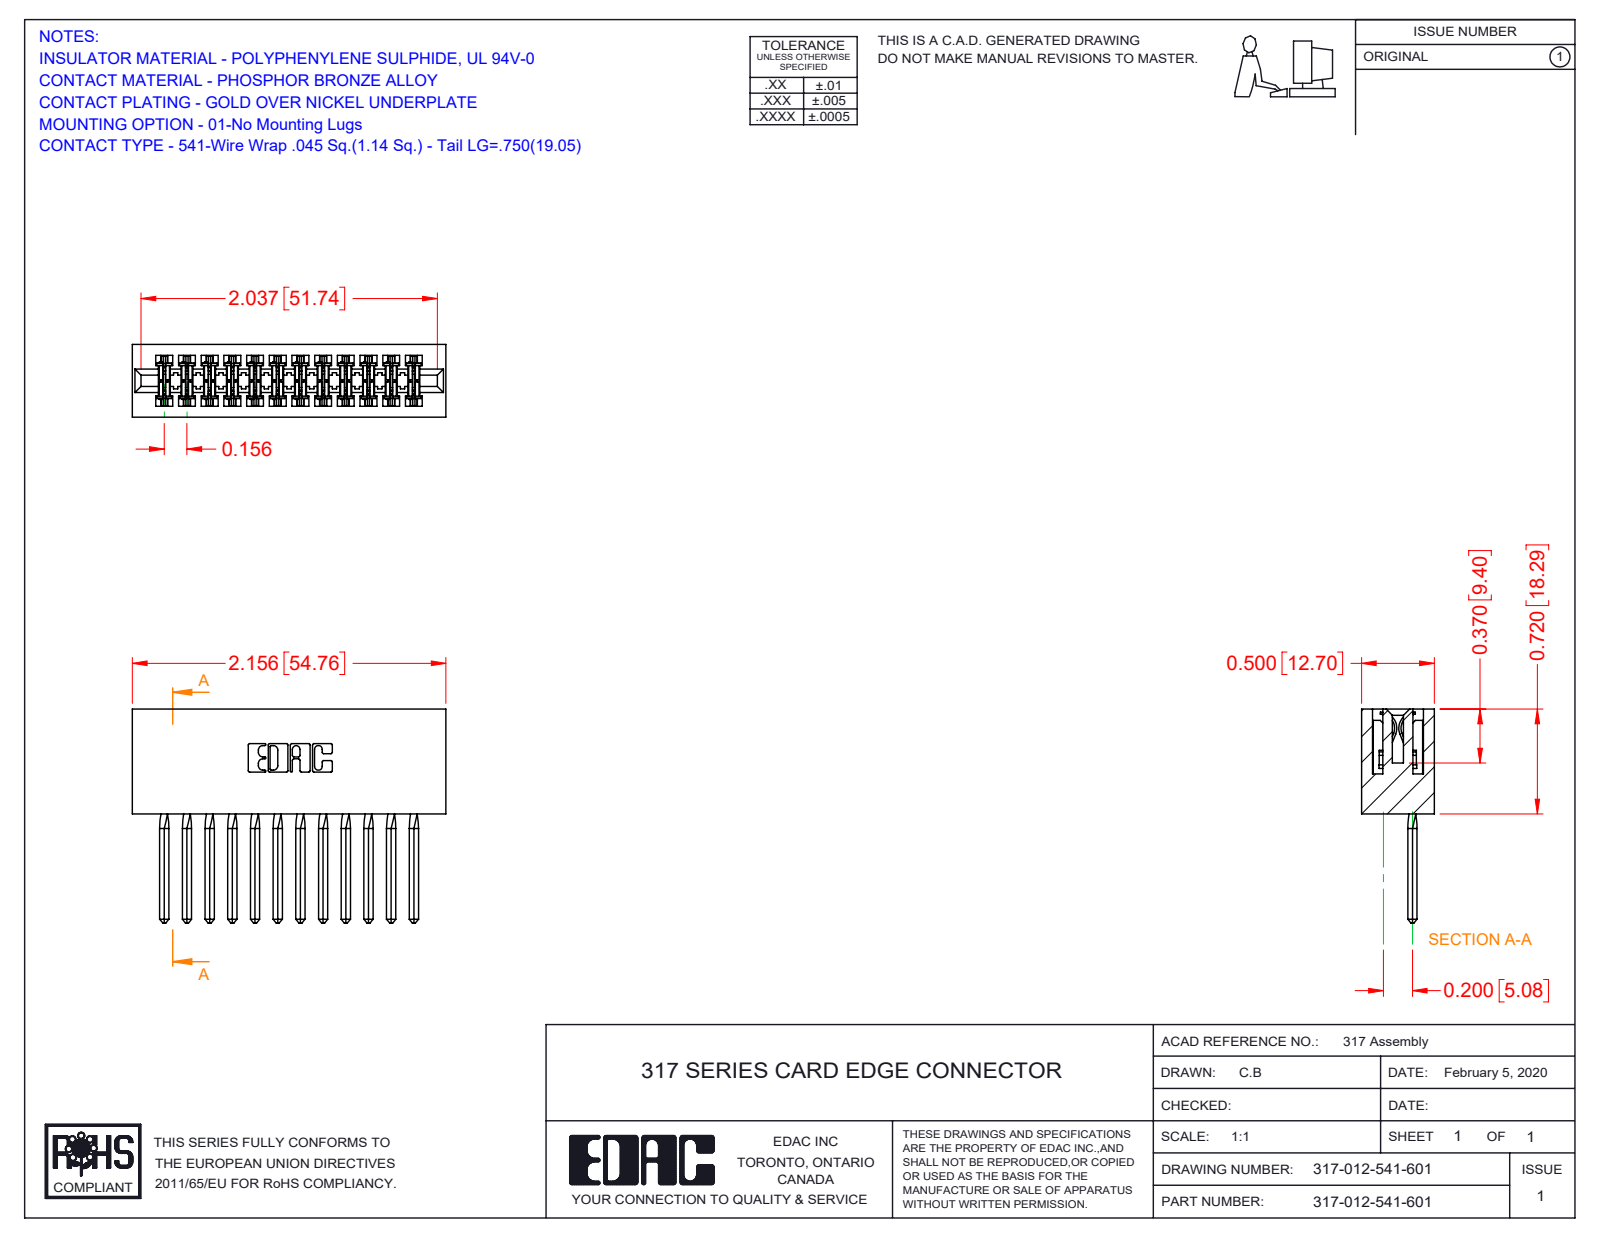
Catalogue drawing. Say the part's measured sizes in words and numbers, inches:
The part is named "317-012-541-601; 317-290-002_541; 317 Part_Lugless". Its 3-D file was written by "SolidWorks 2016 (CONFIG_CONTROL_DESIGN)". It is 13 solids with 1914 faces: 1538 planar, 328 cylindrical and 48 other. Overall it measures 2.156 by 1.47 by 0.5 inches. Its volume is 0.59 cubic inches and its surface area 19.92 square inches. Partial cylindrical surfaces (rounded edges, fillets, slot ends): 24 of radius 0.015, 22 of radius 0.01, 6 of radius 0.007, 6 of radius 0.031, 3 of radius 0.026, 2 of radius 0.095, 2 of radius 0.1, 2 of radius 0.11. The main face-to-face distances are 0.5, 0.075, 0.425, 0.11, 0.22, 0.065, 0.156, 0.35, 0.331, 0.195.
